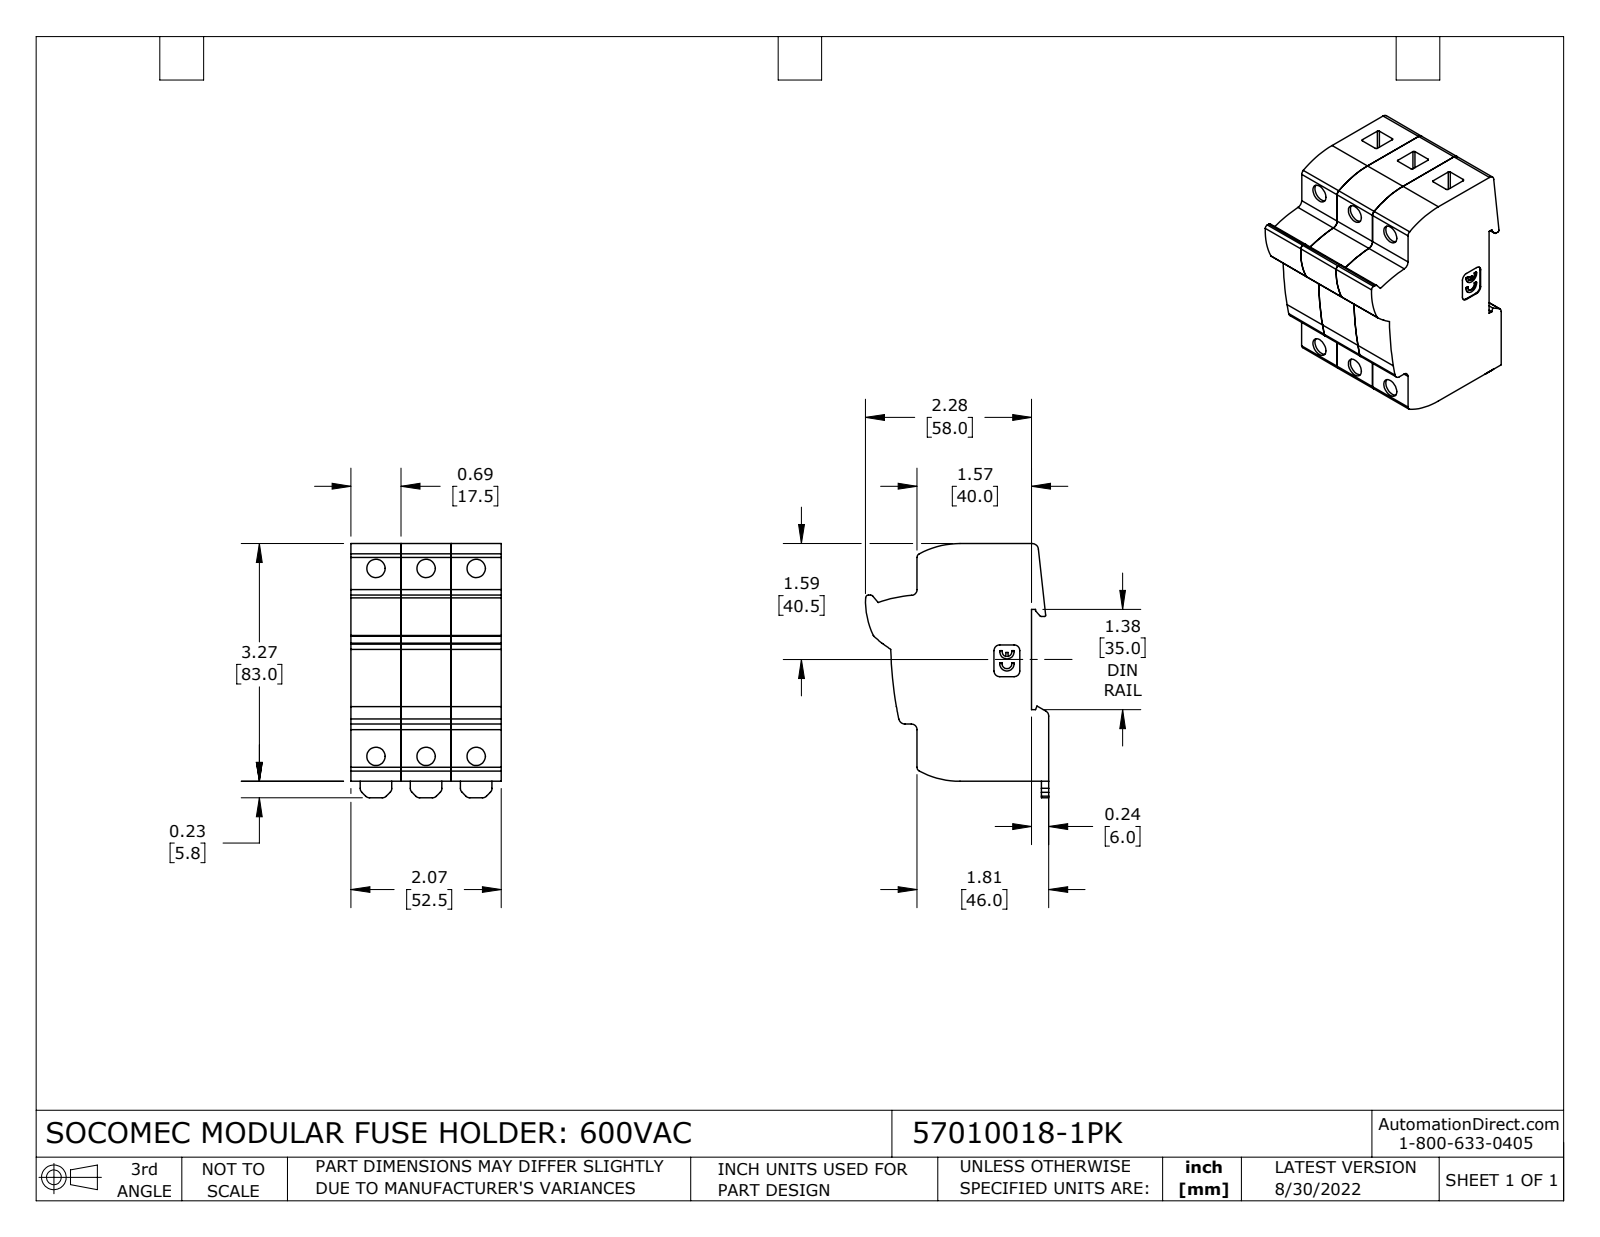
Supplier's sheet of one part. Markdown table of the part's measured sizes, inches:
| quantity | value |
| --- | --- |
| part name | 57010018-1PK |
| STEP written by | SolidWorks 2021 (CONFIG_CONTROL_DESIGN) |
| units | inches |
| bodies | 3 solids, 315 faces (156 planar, 159 cylindrical, 0 other) |
| overall size | 3.496 × 2.52 × 2.067 |
| volume | 12.69 in³ |
| surface area | 64 in² |
| round holes (diameter × count) | 0.252 × 6 |
| partial cylindrical surfaces (radius × count) | 0.079 × 19, 0.02 × 13, 0.039 × 4, 0.059 × 2, 0.067 × 2, 0.087 × 2, 0.098 × 2, 1.186 × 2 |
| main face-to-face distances | 0.689, 1.378, 2.067, 0.236, 1.575, 3.268, 1.811, 0.199, 0.49, 0.888 |
| hole center spacings | 0.689, 2.673, 2.583, 1.378, 2.927 |
